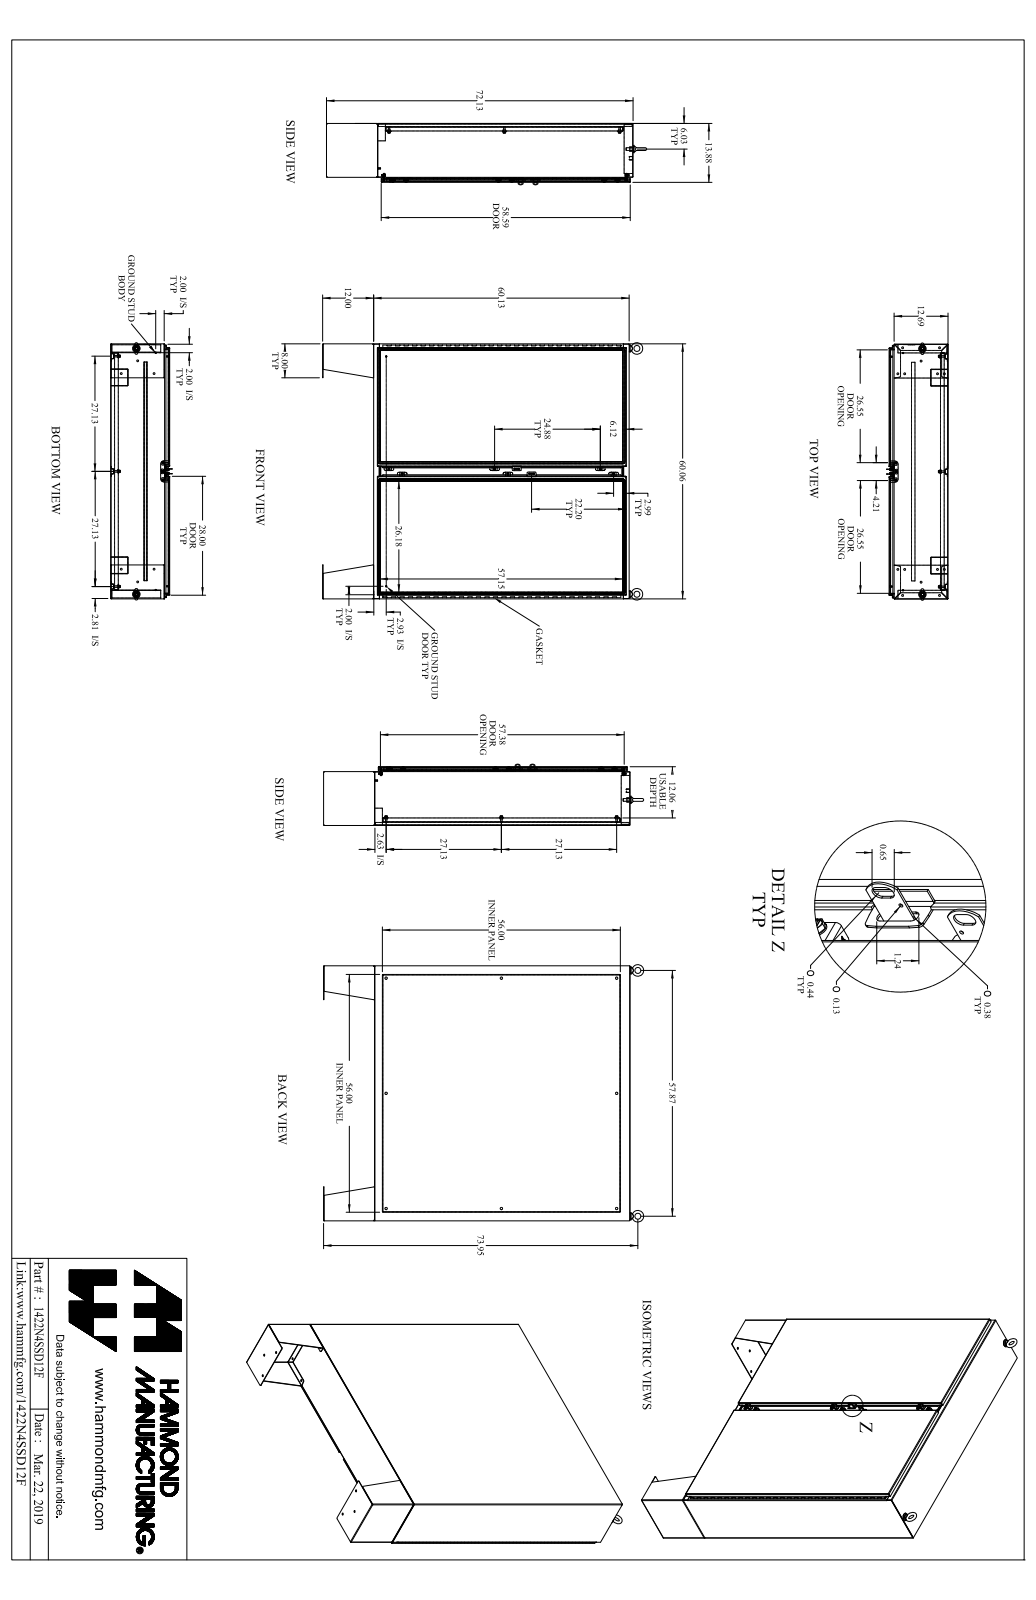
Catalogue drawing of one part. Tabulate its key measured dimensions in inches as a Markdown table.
| quantity | value |
| --- | --- |
| part name | 1422N4SSD12F_Default |
| STEP written by | SolidWorks 2019 (CONFIG_CONTROL_DESIGN) |
| units | inches |
| bodies | 107 solids, 3390 faces (1754 planar, 1440 cylindrical, 196 other) |
| overall size | 75.784 × 61.121 × 14.468 |
| volume | 1 691 in³ |
| surface area | 34 067 in² |
| round holes (diameter × count) | 0.304 × 20, 0.437 × 14, 0.307 × 8, 0.563 × 8, 0.213 × 6, 0.265 × 6, 0.375 × 6, 0.445 × 6, 0.201 × 3, 0.25 × 3, 0.313 × 3, 0.11 × 2 |
| round bosses / shafts (diameter × count) | 1 × 8, 0.65 × 8, 0.375 × 8, 0.332 × 8, 0.5 × 6, 0.39 × 6, 0.244 × 6, 0.313 × 4 |
| partial cylindrical surfaces (radius × count) | 0.048 × 67, 0.143 × 67, 0.25 × 34, 0.06 × 18, 0.116 × 12, 0.141 × 12, 0.185 × 12, 0.05 × 8 |
| main face-to-face distances | 0.095, 13.78, 13.685, 13.875, 0.125, 11.998, 12.093, 1.687, 1.782, 12.218 |
| hole center spacings | 6, 58.513, 12, 59.429, 18, 60.924, 24, 62.959 |
